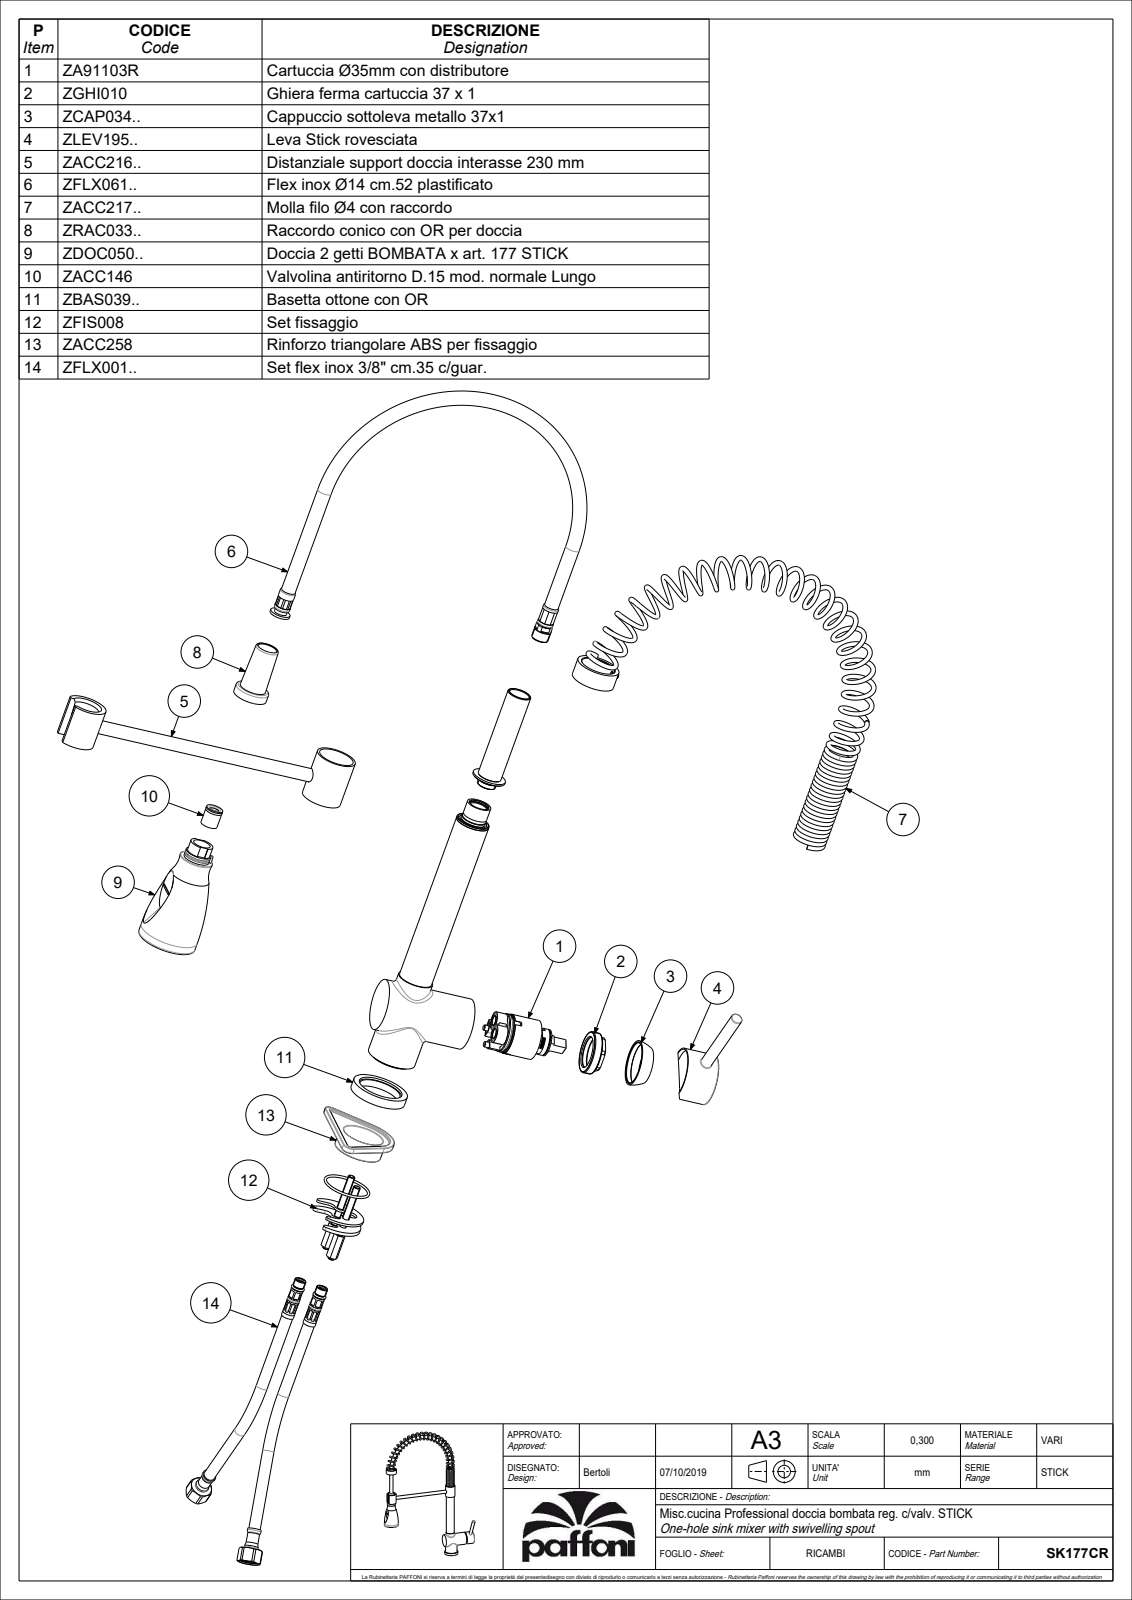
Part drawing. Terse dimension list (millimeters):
name: SK177CR
written by: CREO PARAMETRIC BY PTC INC, 2020044 (CONFIG_CONTROL_DESIGN)
unit: mm
bodies: 1 solid, 416 faces (105 planar, 159 cylindrical, 152 other)
size: 511.14 × 350.09 × 76.17
volume: 694 214 mm³; area: 169 317 mm²
holes: 1× ⌀3, 1× ⌀5.6, 1× ⌀6, 1× ⌀12, 1× ⌀15.2, 1× ⌀17, 1× ⌀18.6, 1× ⌀26
bosses: 32× ⌀2, 2× ⌀13.5, 1× ⌀52, 1× ⌀49.5, 1× ⌀45, 1× ⌀44.5, 1× ⌀43, 1× ⌀38
rounds: 8× R0.5, 2× R1, 1× R2, 1× R2.25, 1× R2.75, 1× R10.15, 1× R17.5
face distances: 138.3, 342.5, 204.2, 357.5, 219.2, 15, 228, 108.2, 336.2, 322
